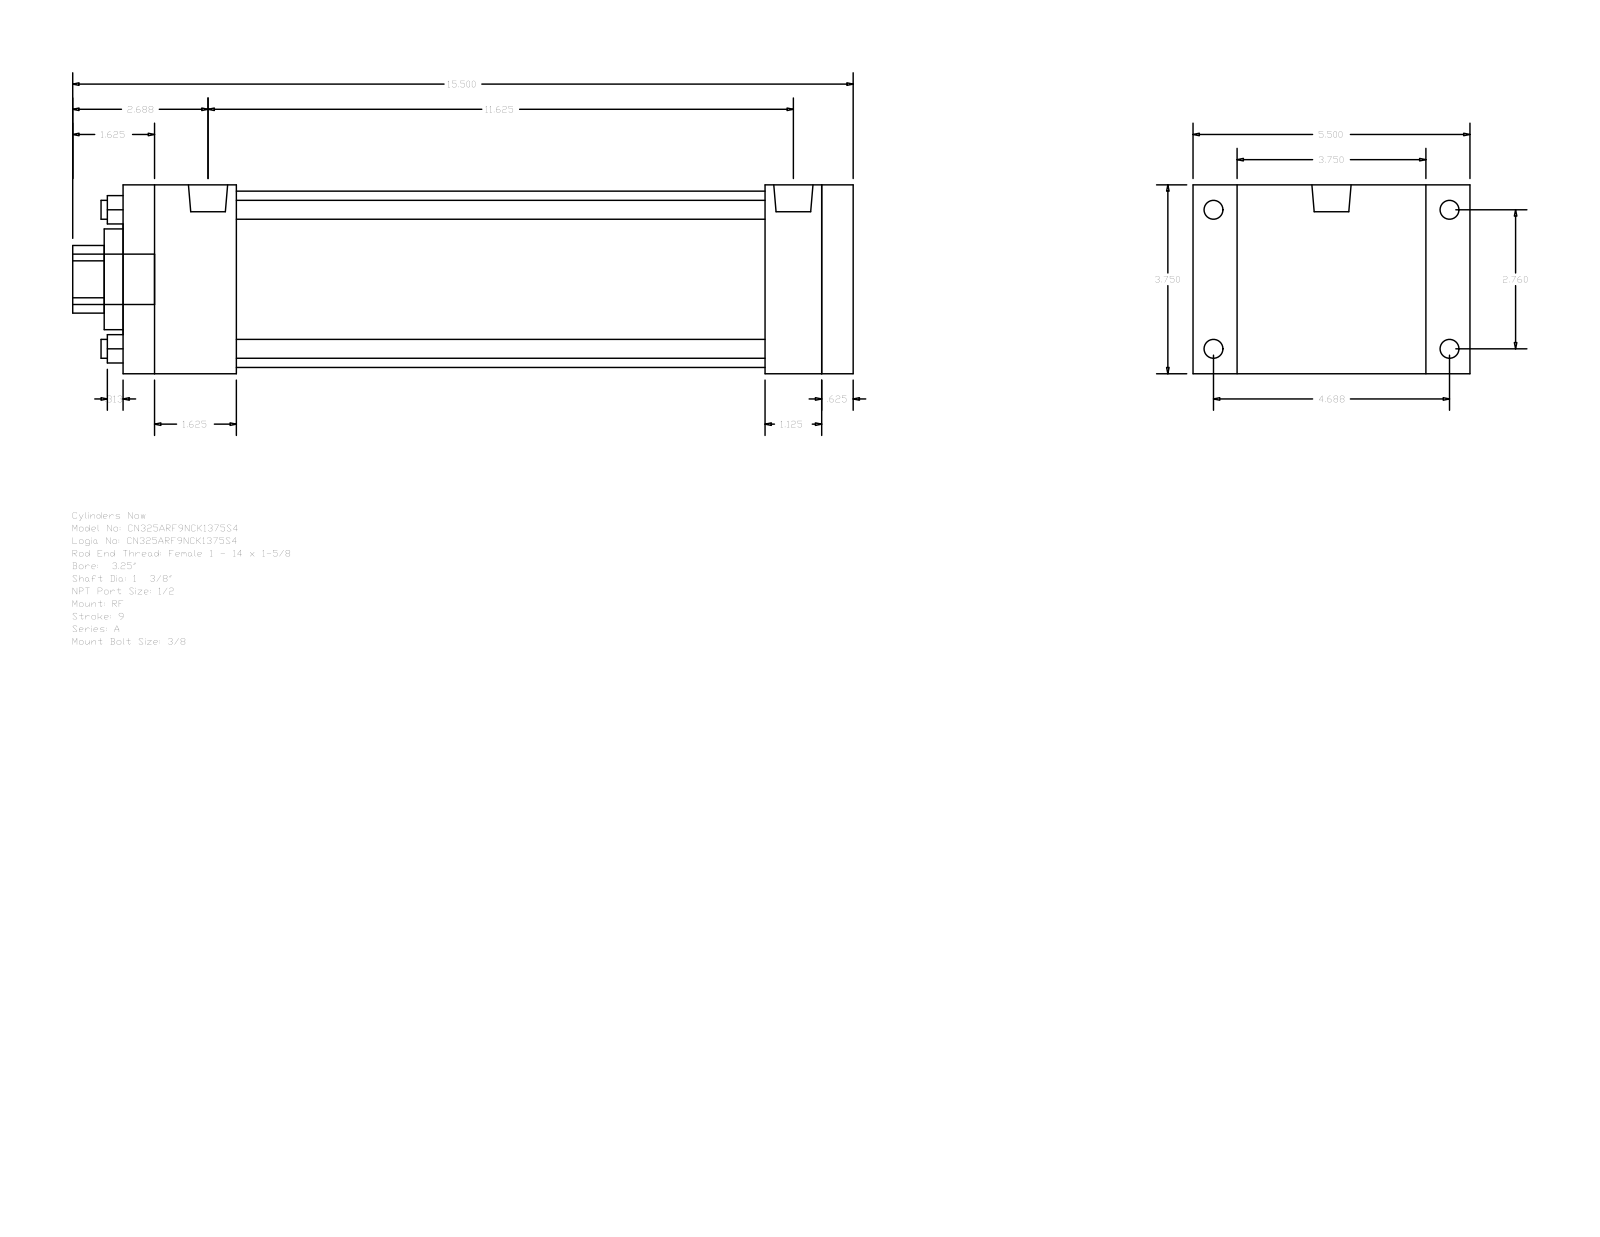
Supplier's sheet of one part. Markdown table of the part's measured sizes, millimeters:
| quantity | value |
| --- | --- |
| part name | A_RF__0325_1.375 |
| STEP written by | GSSL Pune (CONFIG_CONTROL_DESIGN) |
| units | millimeters |
| bodies | 0 solids, 92 faces (64 planar, 28 cylindrical, 0 other) |
| overall size | 393.7 × 139.7 × 95.25 |
| round holes (diameter × count) | 9.53 × 4, 34.92 × 1, 50.8 × 1, 88.9 × 1 |
| round bosses / shafts (diameter × count) | 9.53 × 4, 8.73 × 4, 19.77 × 2, 25.4 × 1 |
| partial cylindrical surfaces (radius × count) | 17.06 × 1 |
| main face-to-face distances | 95.24, 368.3, 15.88, 352.42, 22.23, 117.47, 28.57, 323.85, 44.45, 57.15 |
| hole center spacings | 49.57, 70.1, 99.14 |
